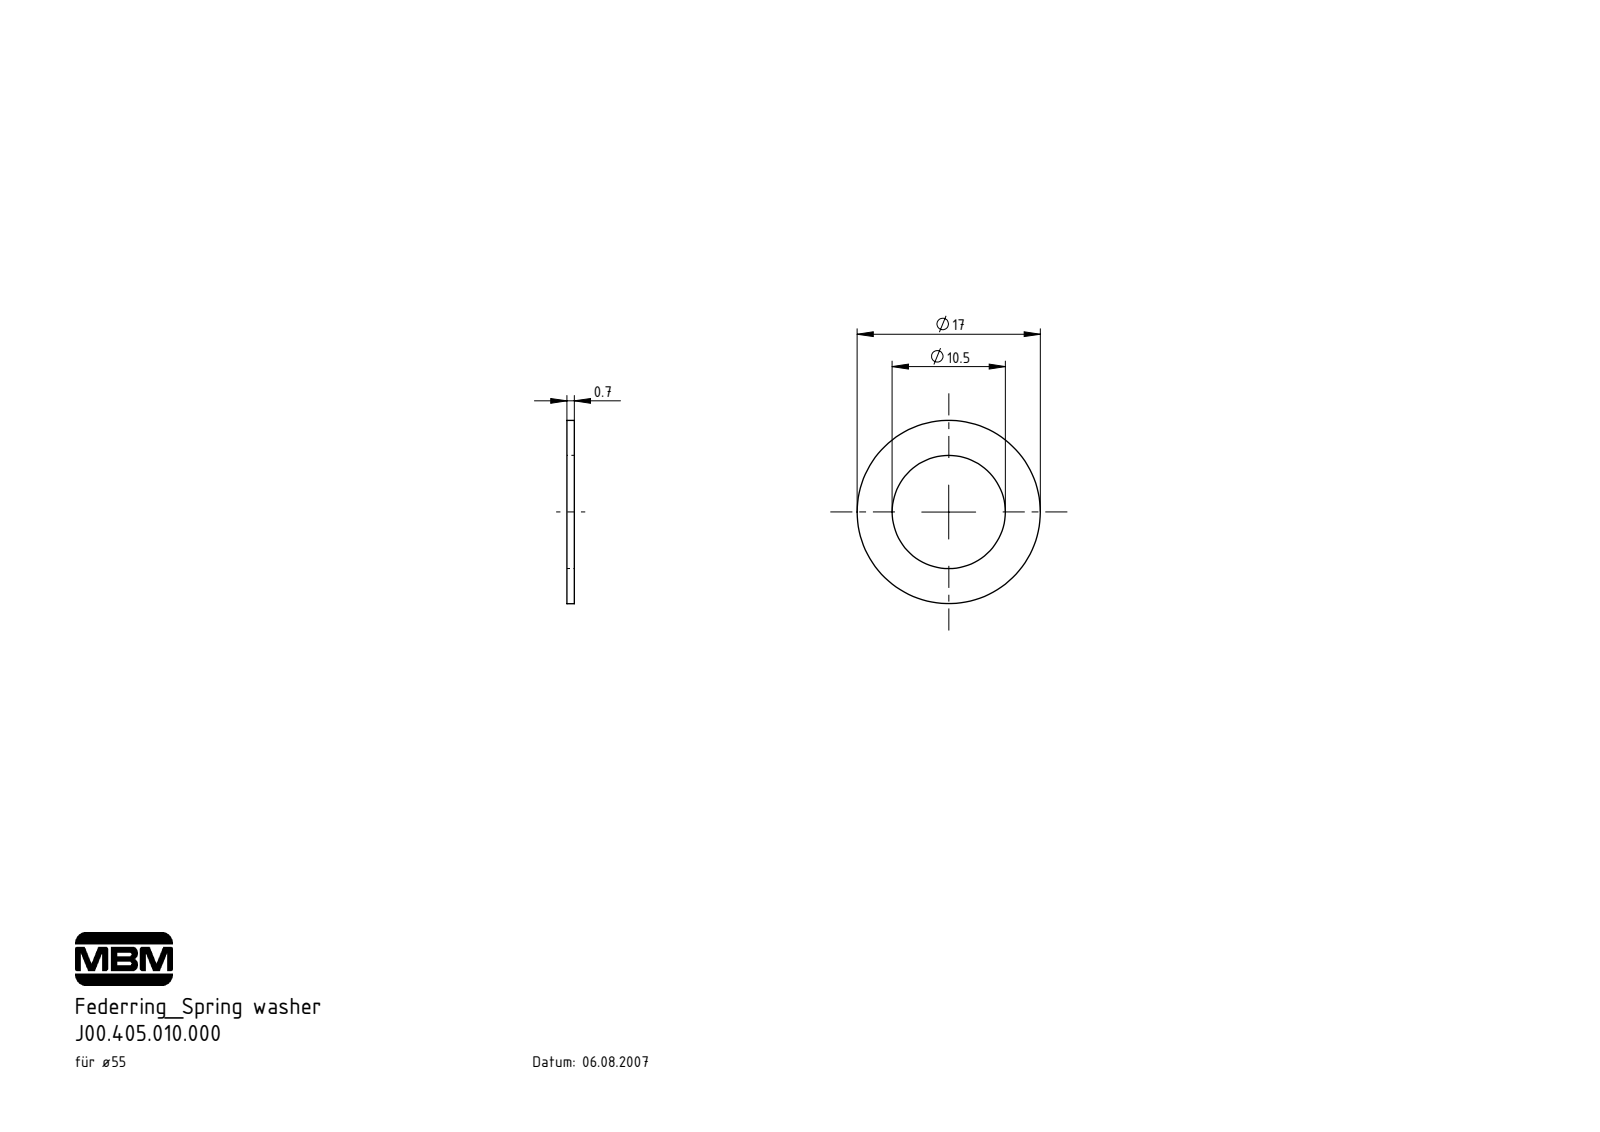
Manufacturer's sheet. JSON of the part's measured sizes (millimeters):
{"part_name": "J00.405.010.000", "step_written_by": "SolidWorks 2022 (AUTOMOTIVE_DESIGN)", "units": "millimeters", "bodies": {"solids": 1, "faces": 6, "planar": 2, "cylindrical": 4, "other": 0}, "overall_size": [17, 17, 0.7], "volume_mm3": 98, "surface_area_mm2": 341, "round_holes": [[10.5, 1]], "round_bosses_or_shafts": [[17, 1]], "face_to_face_distances": [0.7]}
